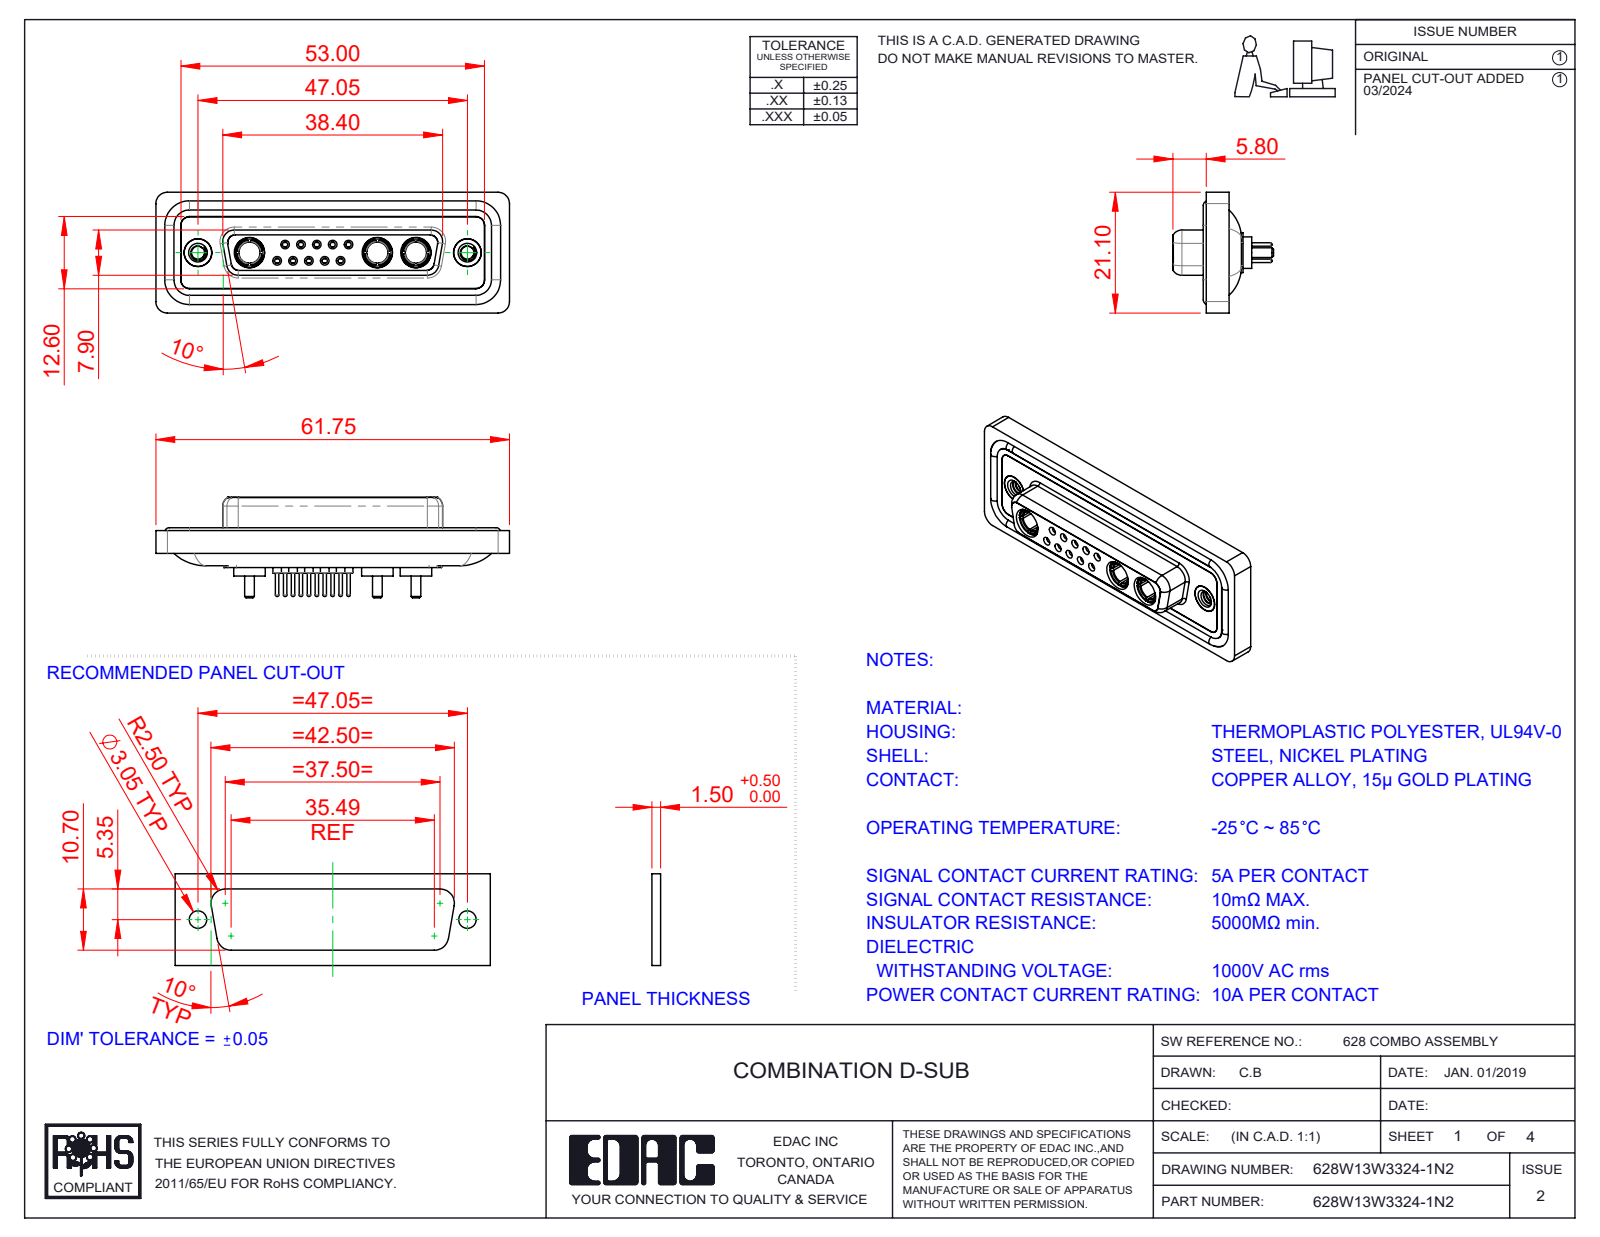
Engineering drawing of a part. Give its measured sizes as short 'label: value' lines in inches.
name: Power Socket_10A S; 628Combo Threaded Rivet_2; 628Combo Shell Front_25 Contacts; 628W13W3324-1N2 (+5 more)
written by: SolidWorks 2023 (CONFIG_CONTROL_DESIGN)
unit: in
bodies: 23 solids, 1158 faces (342 planar, 447 cylindrical, 369 other)
size: 2.431 × 0.831 × 0.691
volume: 0.502 in³; area: 21.19 in²
holes: 10× ⌀0.035, 10× ⌀0.043, 10× ⌀0.059, 10× ⌀0.079, 5× ⌀0.063, 5× ⌀0.067, 5× ⌀0.191, 3× ⌀0.146, 3× ⌀0.209, 2× ⌀0.089, 2× ⌀0.157, 2× ⌀0.159
bosses: 10× ⌀0.087, 10× ⌀0.024, 9× ⌀0.063, 3× ⌀0.217, 3× ⌀0.205, 3× ⌀0.195, 3× ⌀0.187, 3× ⌀0.148
rounds: 22× R0.059, 18× R0.079, 8× R0.053, 8× R0.063, 4× R0.01, 4× R0.02, 4× R0.024, 4× R0.026
face distances: 0.016, 0.071, 0.293, 0.222, 0.02, 0.26, 0.278, 0.063, 0.114, 0.043
hole spacings: 0.124, 0.109, 0.198, 0.198, 0.218, 0.327, 0.295, 0.109
